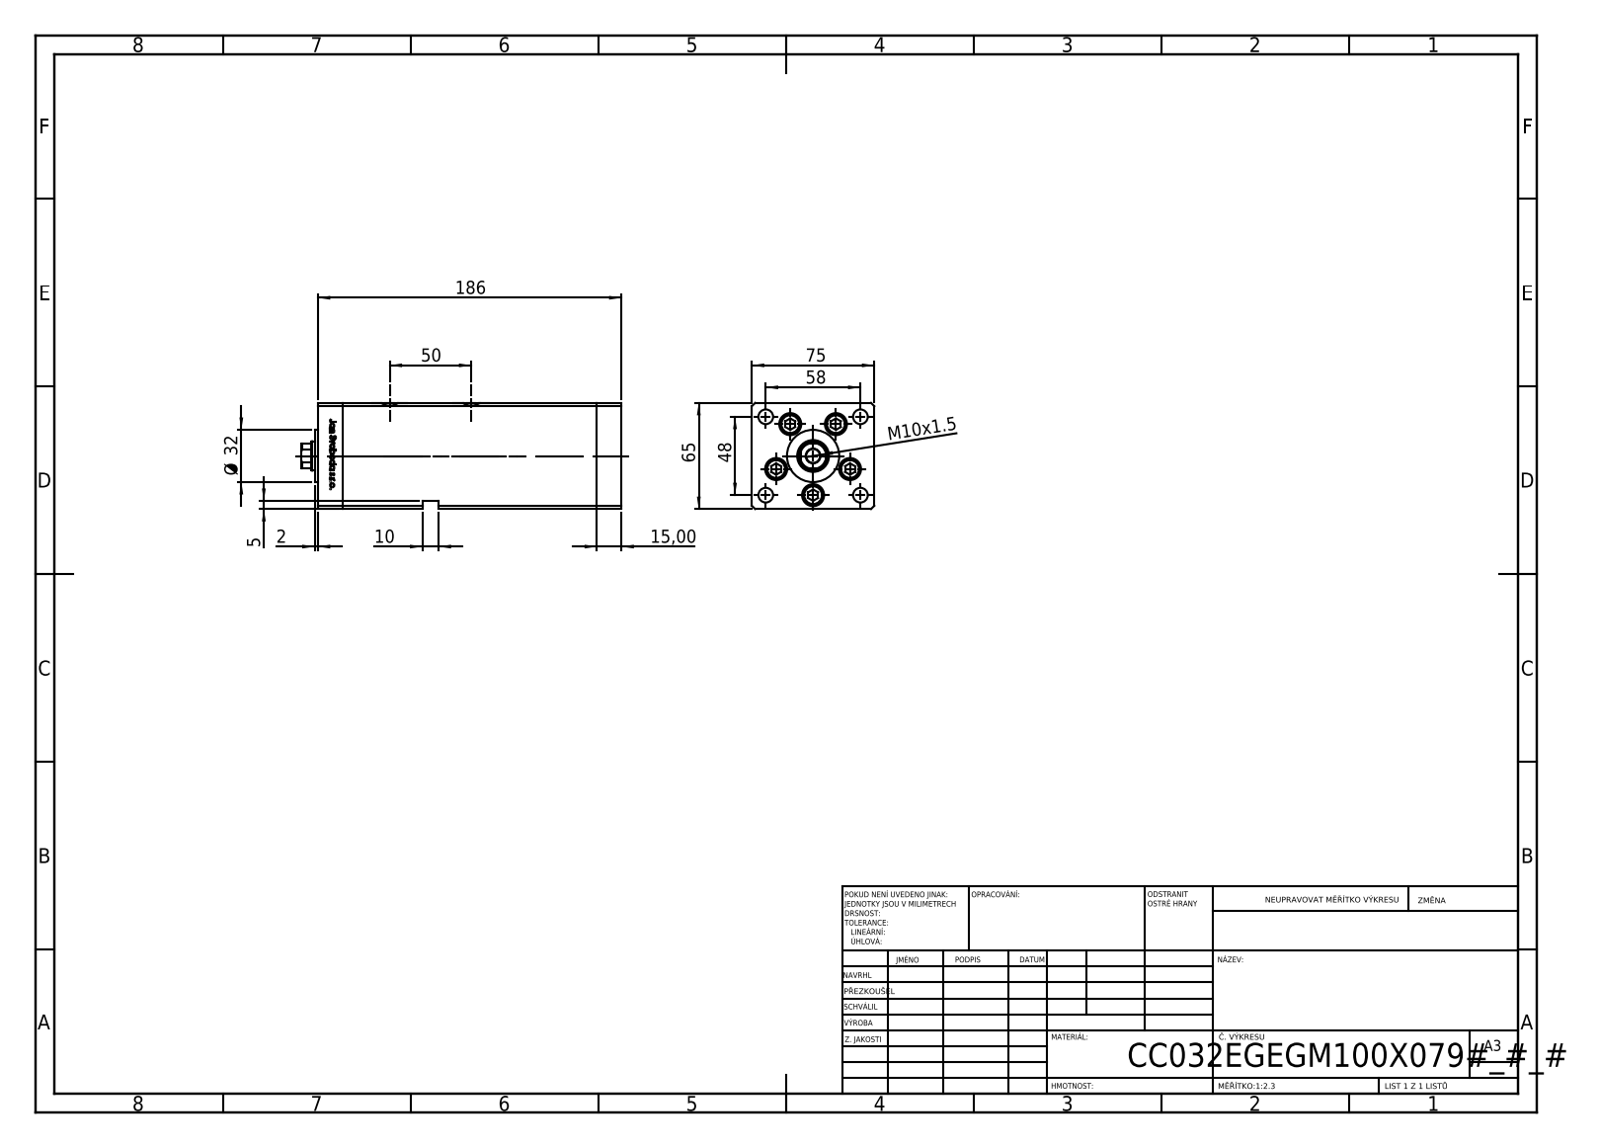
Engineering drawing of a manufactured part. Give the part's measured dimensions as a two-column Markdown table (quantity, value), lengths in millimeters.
| quantity | value |
| --- | --- |
| part name | V220C_E MIDDLE; V220C_FRONT_E; V220C BACK_E; V220C_VC_E (+1 more) |
| STEP written by | SolidWorks 2019 (CONFIG_CONTROL_DESIGN) |
| units | millimeters |
| bodies | 14 solids, 1212 faces (473 planar, 165 cylindrical, 574 other) |
| overall size | 196 × 75 × 65 |
| volume | 769 603 mm³ |
| surface area | 146 638 mm² |
| round holes (diameter × count) | 9 × 9, 13.5 × 5, 10.5 × 4, 16.5 × 4, 2 × 2, 13.16 × 2, 8.5 × 1, 18 × 1, 19.5 × 1 |
| round bosses / shafts (diameter × count) | 12.5 × 5, 8 × 5, 32 × 1 |
| partial cylindrical surfaces (radius × count) | 0.93 × 2, 8.5 × 1 |
| main face-to-face distances | 75, 65, 15, 156, 171, 186, 28, 54.5, 10.5, 26.25 |
| hole center spacings | 24, 37.64, 58, 15.67, 17.22, 27.71, 28.83, 29 |
